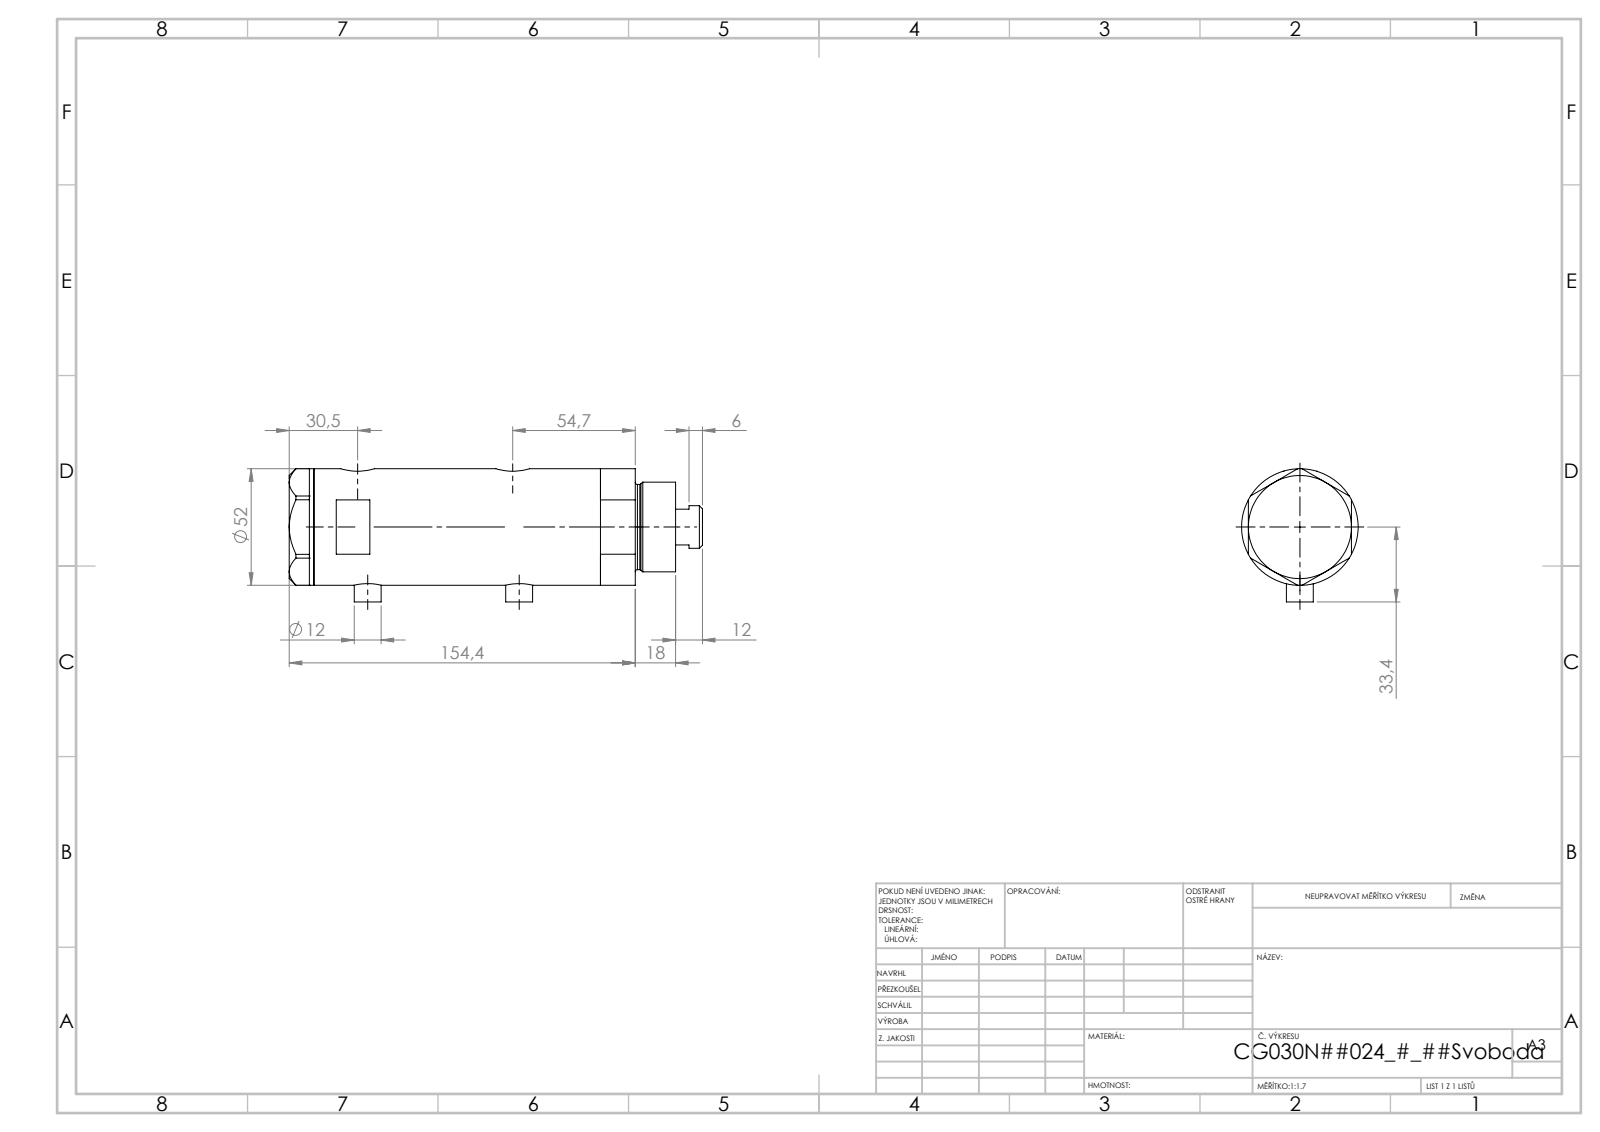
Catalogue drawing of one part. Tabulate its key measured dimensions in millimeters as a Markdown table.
| quantity | value |
| --- | --- |
| part name | V270CG_FRONT; V270CG_VC; V270CG_BACK; V270CG_MIDDLE |
| STEP written by | SolidWorks 2019 (CONFIG_CONTROL_DESIGN) |
| units | millimeters |
| bodies | 4 solids, 140 faces (67 planar, 53 cylindrical, 20 other) |
| overall size | 184.4 × 59.4 × 52 |
| volume | 336 637 mm³ |
| surface area | 77 715 mm² |
| round holes (diameter × count) | 5 × 2, 9.73 × 2, 12.5 × 2, 15 × 2, 6.5 × 1, 20 × 1, 21.5 × 1, 30 × 1, 33 × 1, 44 × 1 |
| round bosses / shafts (diameter × count) | 12 × 2, 52 × 1, 40 × 1, 38 × 1, 19 × 1 |
| main face-to-face distances | 91.5, 23.8, 67.7, 11, 34.8, 102.5, 46, 138.9, 127.9, 104.1 |
| hole center spacings | 2.9, 4.5, 64.7, 67.6, 69.2, 72.1 |
